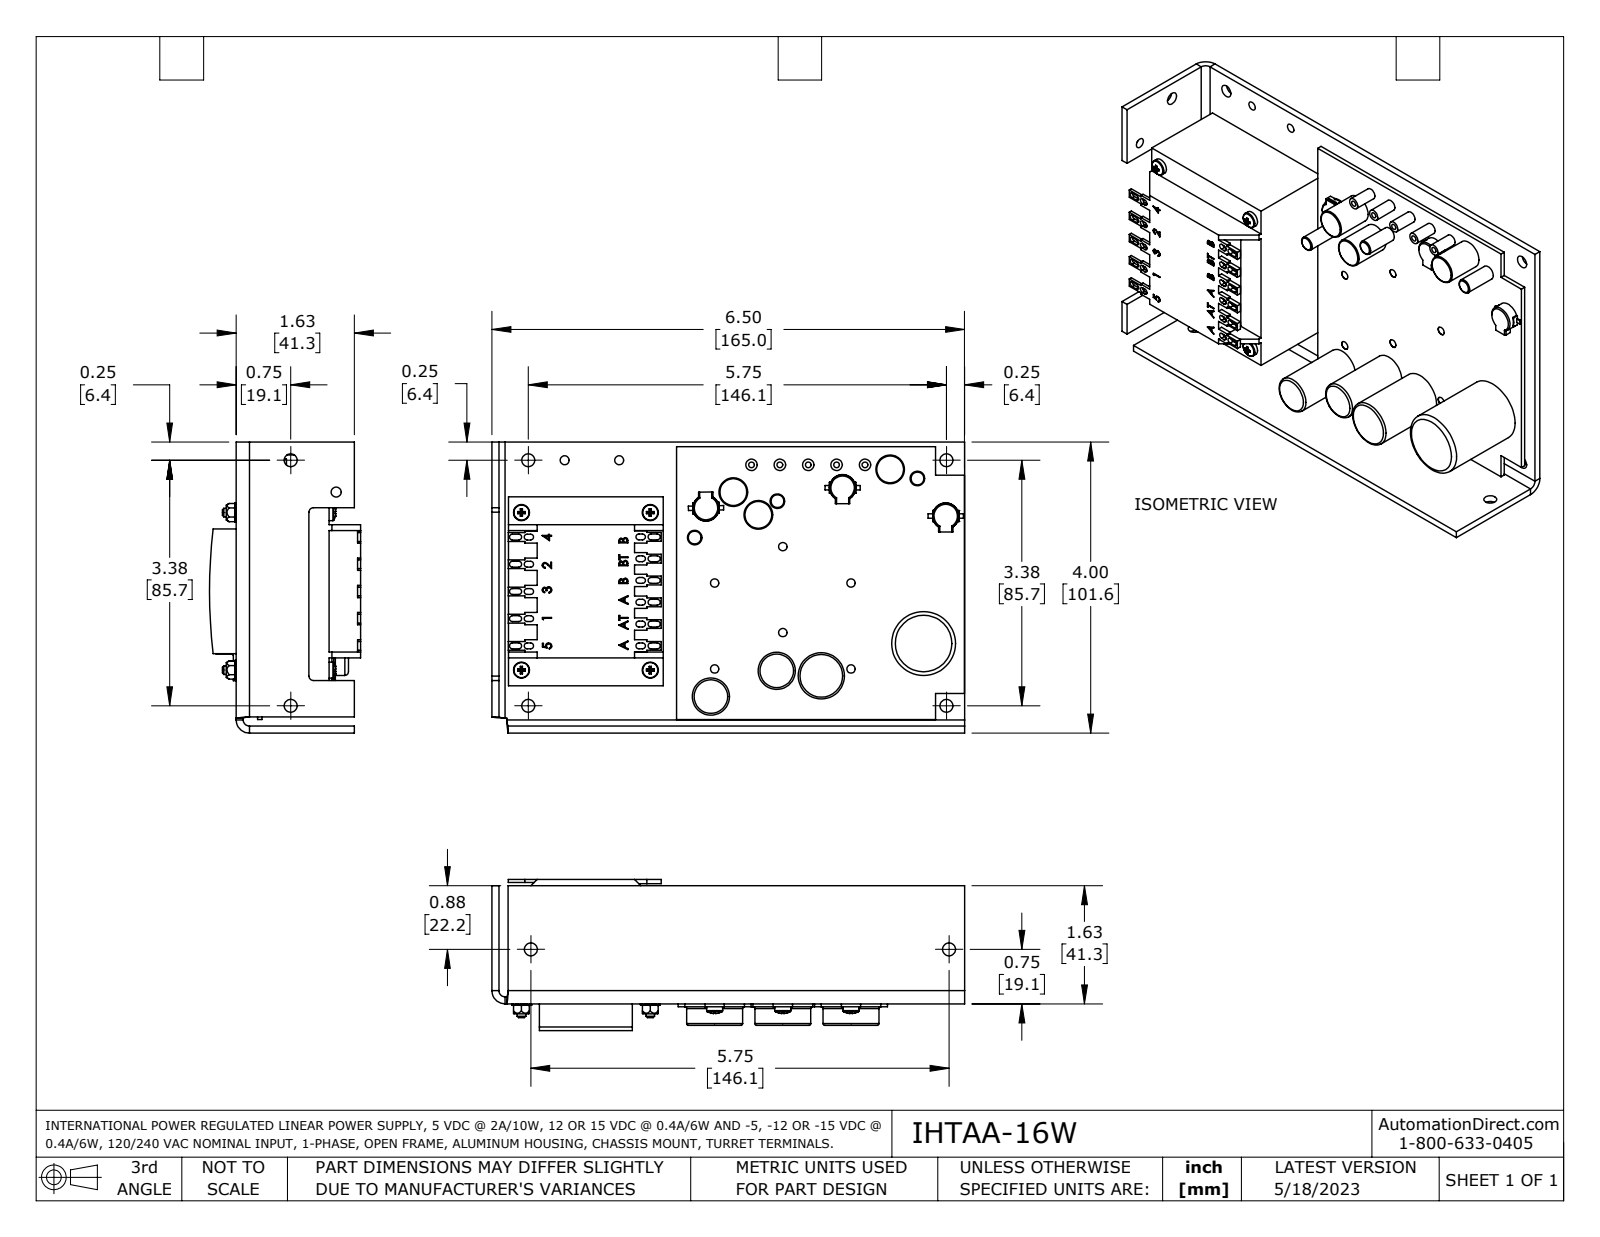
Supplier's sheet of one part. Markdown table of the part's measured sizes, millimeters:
| quantity | value |
| --- | --- |
| part name | IHTAA-16W |
| STEP written by | SolidWorks 2021 (AUTOMOTIVE_DESIGN) |
| units | millimeters |
| bodies | 24 solids, 1165 faces (765 planar, 261 cylindrical, 139 other) |
| overall size | 165.1 × 101.6 × 52.8 |
| volume | 252 500 mm³ |
| surface area | 108 100 mm² |
| round holes (diameter × count) | 4.5 × 8, 2.9 × 6, 2 × 5, 2.5 × 4, 3 × 4, 3.3 × 4, 3.1 × 2, 3.5 × 1 |
| round bosses / shafts (diameter × count) | 5.6 × 10, 6.4 × 6, 3 × 6, 4 × 5, 19.5 × 3, 10 × 3, 5.1 × 3, 13 × 2 |
| partial cylindrical surfaces (radius × count) | 1 × 44, 4.1 × 6, 0.4 × 4, 2.5 × 4, 3.4 × 4, 12.8 × 3, 1.6 × 2, 2.2 × 2 |
| main face-to-face distances | 2.4, 5, 7.4, 1.6, 6.6, 9, 25, 54, 3.4, 5.8 |
| hole center spacings | 27, 30, 85.7, 146.1, 9.9, 9.9, 12.7, 19.8 |
